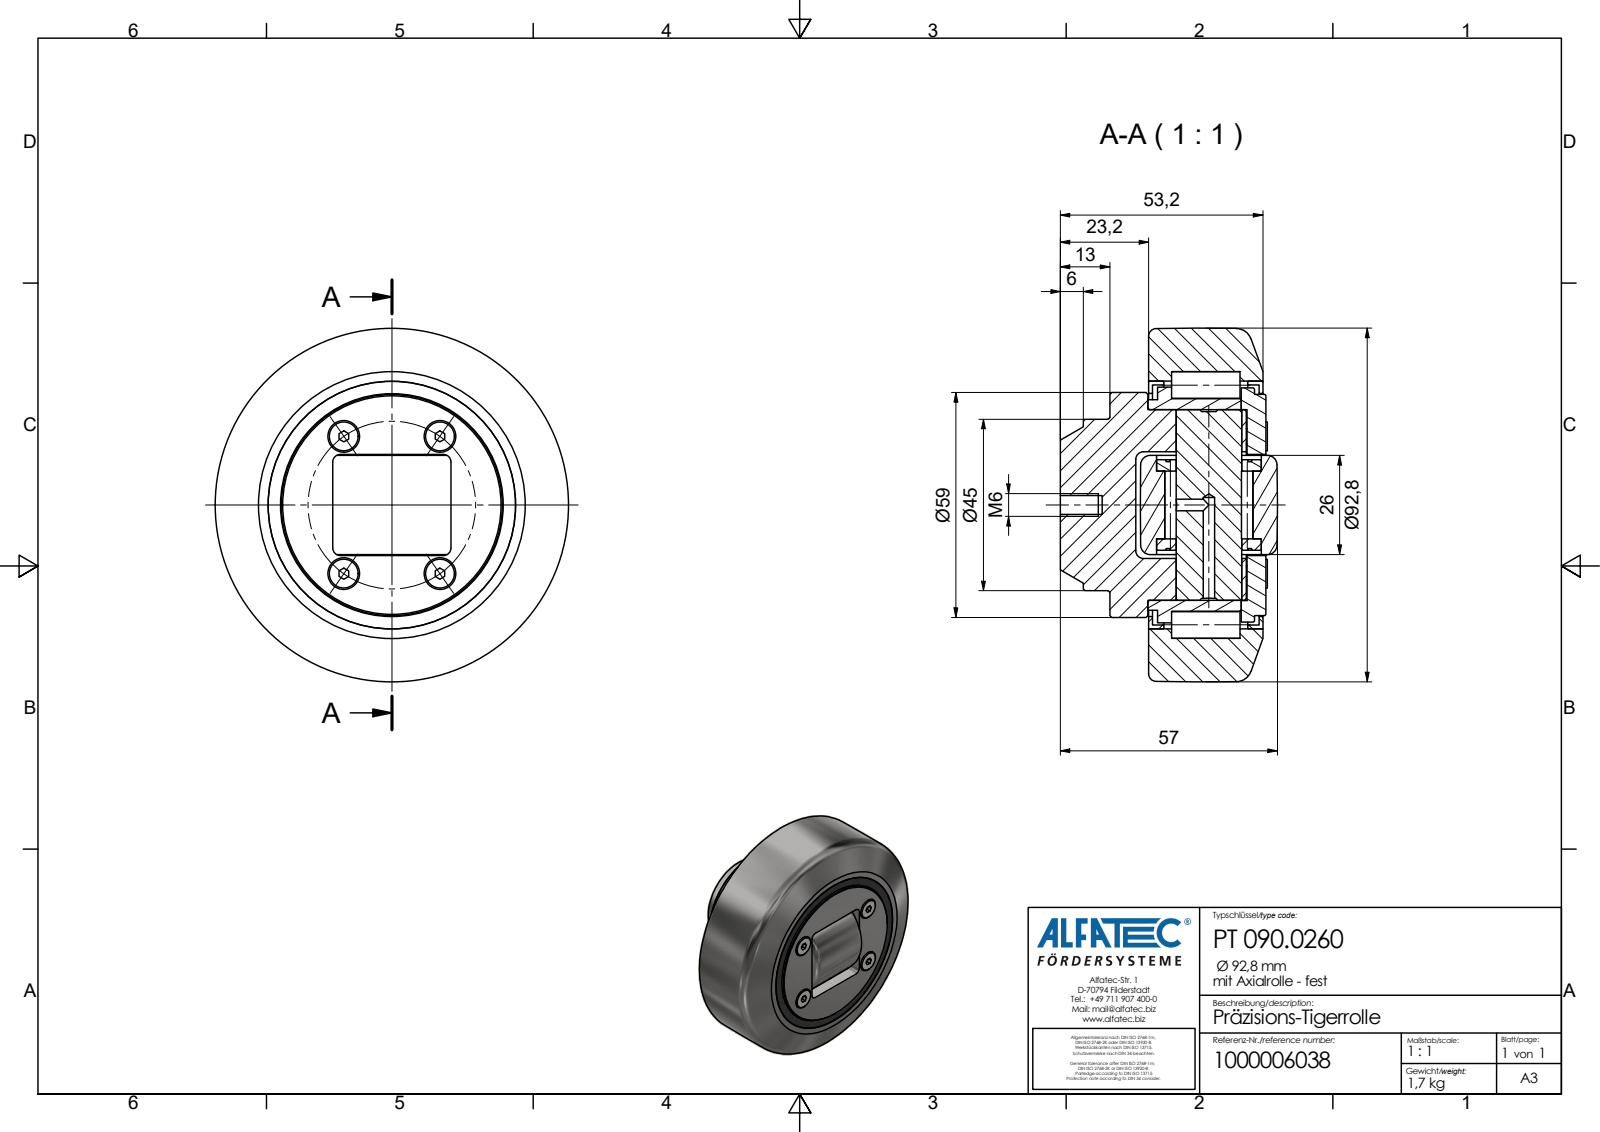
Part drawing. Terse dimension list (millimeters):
name: PT090.0260_Kontur
written by: Autodesk Inventor 2020 (AP242_MANAGED_MODEL_BASED_3D_ENGINEERING_MIM_LF)
unit: mm
bodies: 3 solids, 172 faces (67 planar, 59 cylindrical, 46 other)
size: 92.8 × 92.8 × 57
volume: 202 483 mm³; area: 56 335 mm²
holes: 4× ⌀4.3, 3× ⌀3, 1× ⌀2.5, 1× ⌀4.92, 1× ⌀17.2, 1× ⌀23.2, 1× ⌀27.5, 1× ⌀50, 1× ⌀50.1, 1× ⌀58.5, 1× ⌀63, 1× ⌀65
bosses: 4× ⌀7.53, 4× ⌀4, 1× ⌀61.8, 1× ⌀61.5, 1× ⌀59, 1× ⌀58, 1× ⌀55.8, 1× ⌀55.3
rounds: 8× R2, 2× R1.5, 1× R19
face distances: 5, 6, 24, 30.8, 24.8, 25.8, 4.2, 28, 30, 0.8
hole spacings: 22, 25.24, 36.04, 44
